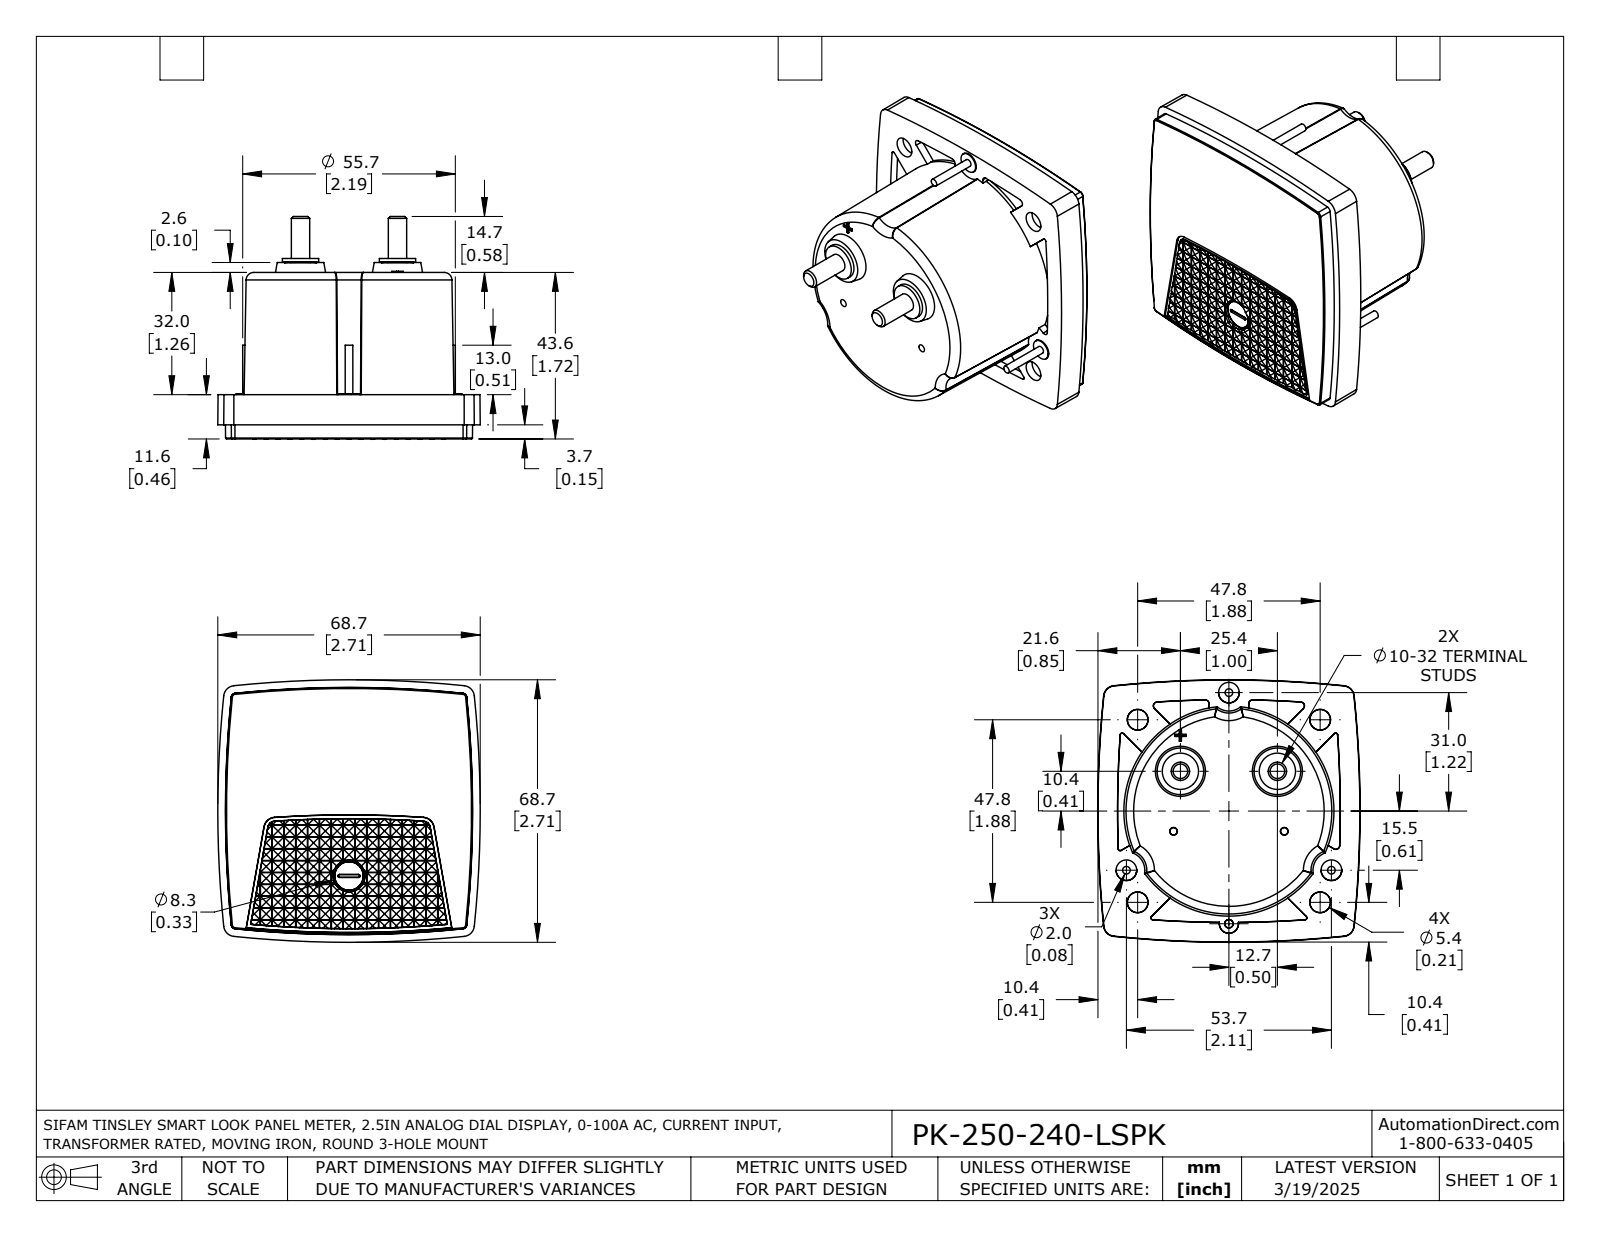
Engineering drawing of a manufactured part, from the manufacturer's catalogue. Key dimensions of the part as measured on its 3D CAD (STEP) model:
Part name (STEP PRODUCT): PK-250-240-LSPK
STEP written by: SolidWorks 2021 (AUTOMOTIVE_DESIGN)
Units: inches
Bodies: 1 solid, 1550 faces (1165 planar, 265 cylindrical, 120 other)
Overall size (bounding box): 2.706 × 2.706 × 2.297
Volume: 7.594 in³ · Surface area: 30.41 in²
Round bosses / shafts (diameter × count): ⌀0.213 ×3, ⌀0.079 ×3, ⌀0.374 ×2, ⌀0.189 ×2, ⌀0.215 ×1
Partial cylindrical surfaces — rounded edges, fillets, slot ends (radius × count): R0.167 ×2, R1.083 ×1
Main face-to-face distances: 1.717, 1.26, 0.457, 0.024, 0.087, 0.096, 0.311, 0.12, 0.072, 1.346
